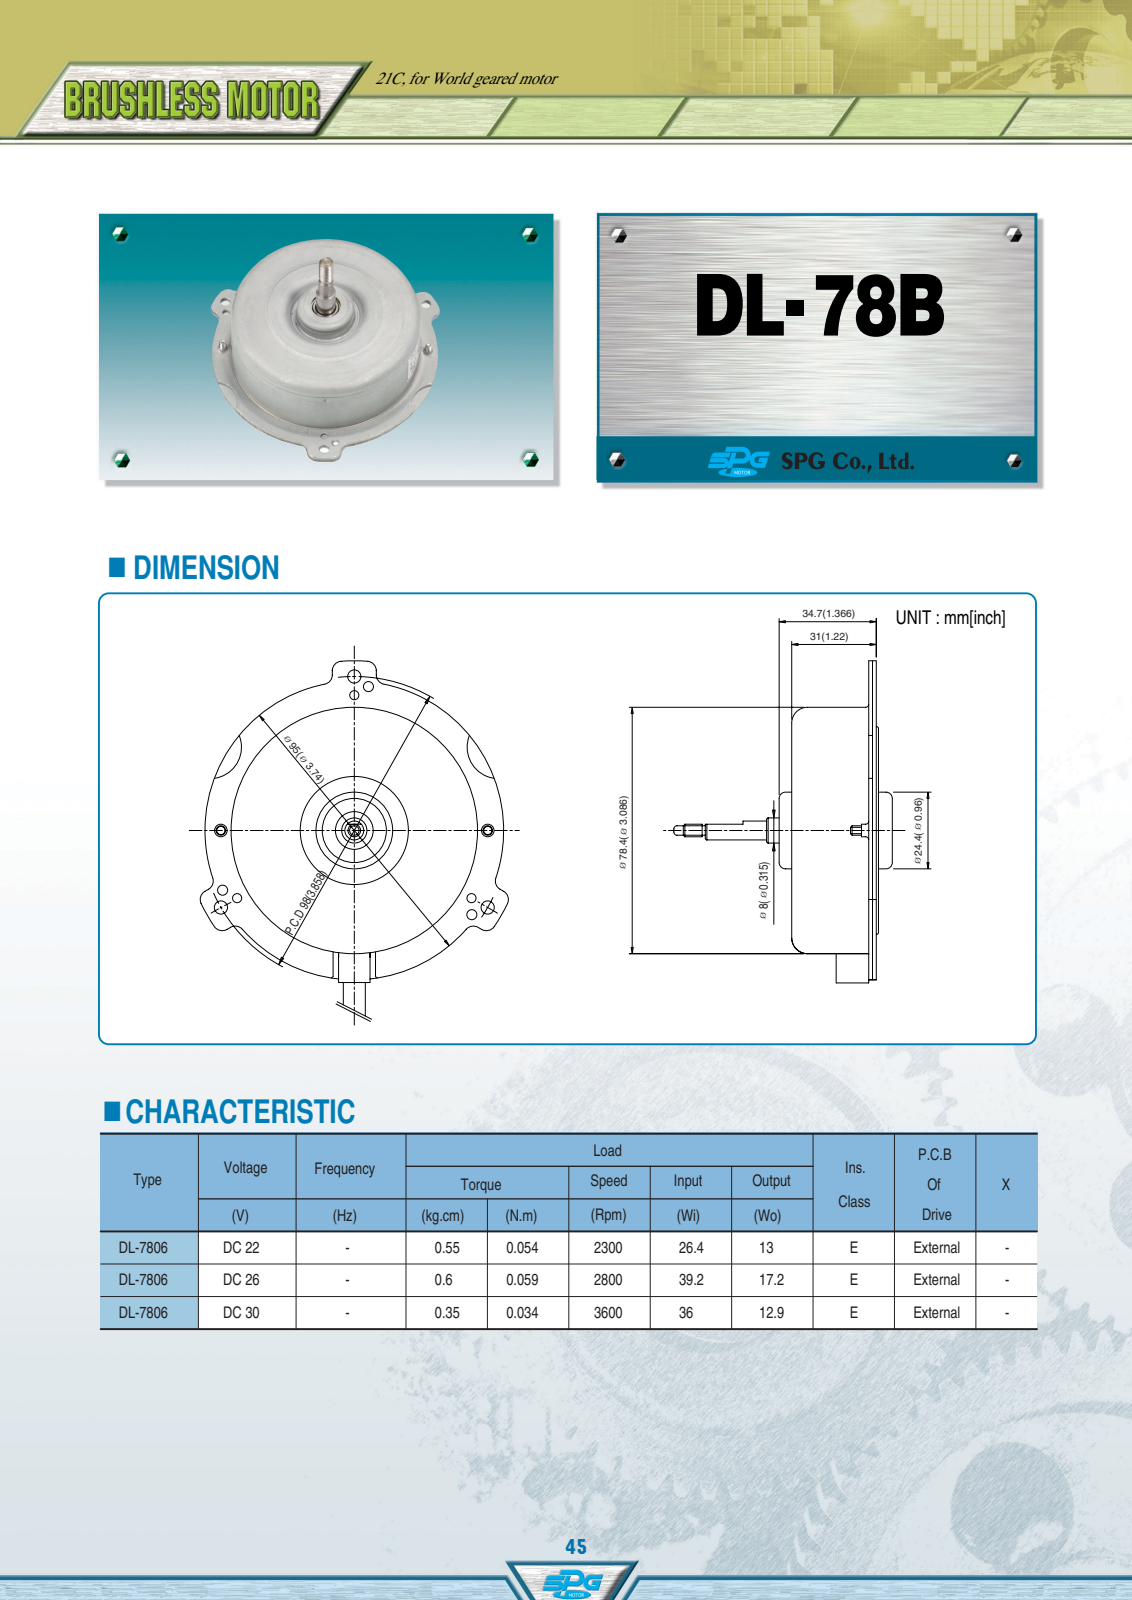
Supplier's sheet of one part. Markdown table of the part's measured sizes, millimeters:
| quantity | value |
| --- | --- |
| part name | 7806_B TYPE |
| STEP written by | Autodesk Inventor 2011 (AUTOMOTIVE_DESIGN) |
| units | millimeters |
| bodies | 1 solid, 181 faces (91 planar, 61 cylindrical, 29 other) |
| overall size | 101.5 × 98.06 × 68.62 |
| volume | 32 638 mm³ |
| surface area | 42 829 mm² |
| round holes (diameter × count) | 2.9 × 4, 4.2 × 3, 2.75 × 2, 4.8 × 2, 5.5 × 1, 9 × 1, 22 × 1, 64 × 1, 76 × 1 |
| round bosses / shafts (diameter × count) | 4.15 × 2, 95 × 1, 78.4 × 1, 66.4 × 1, 24.4 × 1, 20 × 1, 8 × 1, 5 × 1 |
| partial cylindrical surfaces (radius × count) | 3 × 12, 0.5 × 4, 4 × 2, 10 × 2, 4.8 × 1, 5 × 1, 37.8 × 1, 38.7 × 1 |
| main face-to-face distances | 1.2, 31.7, 0.7, 31, 1.9, 29.8, 32.2, 0.5, 32.9, 30.5 |
| hole center spacings | 79.78, 43.05, 74.56, 49, 5.95, 5.96, 22.27, 24.51 |
